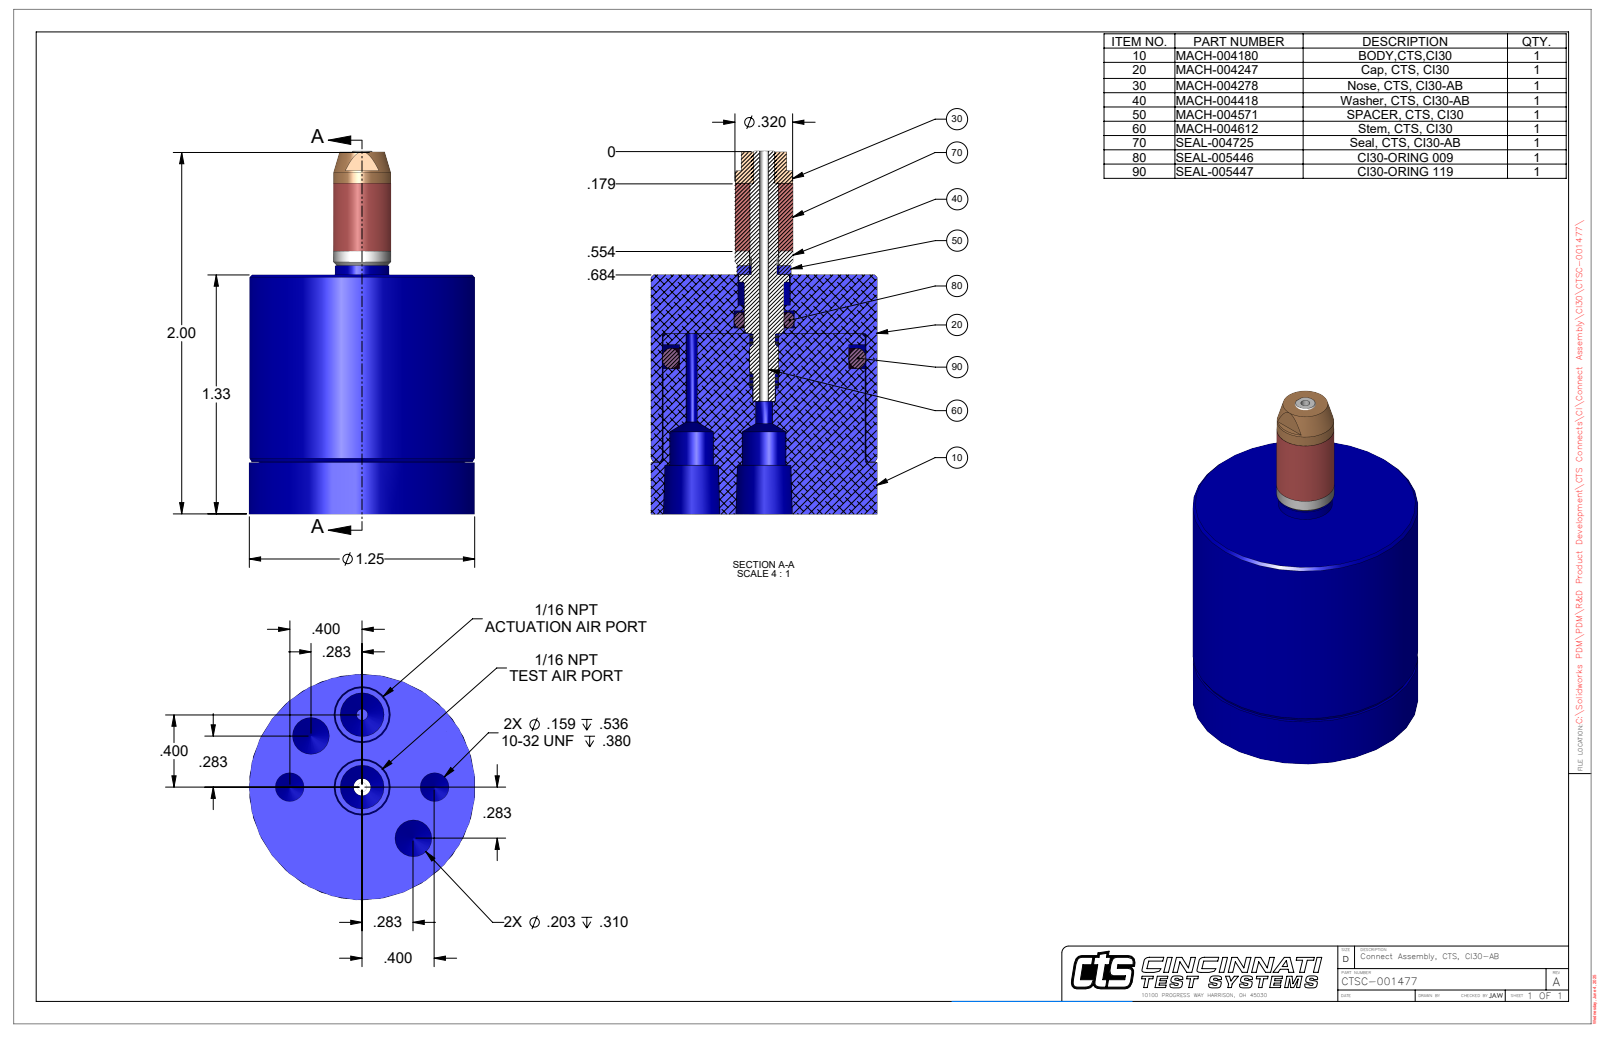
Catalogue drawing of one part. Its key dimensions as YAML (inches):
part_name: "CTSC-001477"
step_written_by: "SolidWorks 2023 (AUTOMOTIVE_DESIGN)"
units: inches
bodies: {solids: 1, faces: 89, planar: 22, cylindrical: 36, other: 31}
overall_size: [2.009, 1.25, 1.25]
volume: 1.564
surface_area: 13.11
round_holes:
  - {diameter: 0.159, count: 2}
  - {diameter: 0.203, count: 2}
  - {diameter: 0.242, count: 2}
  - {diameter: 0.052, count: 1}
  - {diameter: 0.062, count: 1}
  - {diameter: 0.094, count: 1}
  - {diameter: 0.289, count: 1}
  - {diameter: 1.125, count: 1}
round_bosses_or_shafts:
  - {diameter: 1.25, count: 1}
  - {diameter: 1.115, count: 1}
  - {diameter: 0.32, count: 1}
  - {diameter: 0.317, count: 1}
  - {diameter: 0.3, count: 1}
  - {diameter: 0.277, count: 1}
face_to_face_distances: [1.325, 0.287, 1.039, 0.29, 1.035, 0.271, 0.015, 0.019, 1.054, 2.004]
hole_center_spacings: [0.306, 0.4, 0.739, 0.4, 0.566, 0.8, 0.8]
